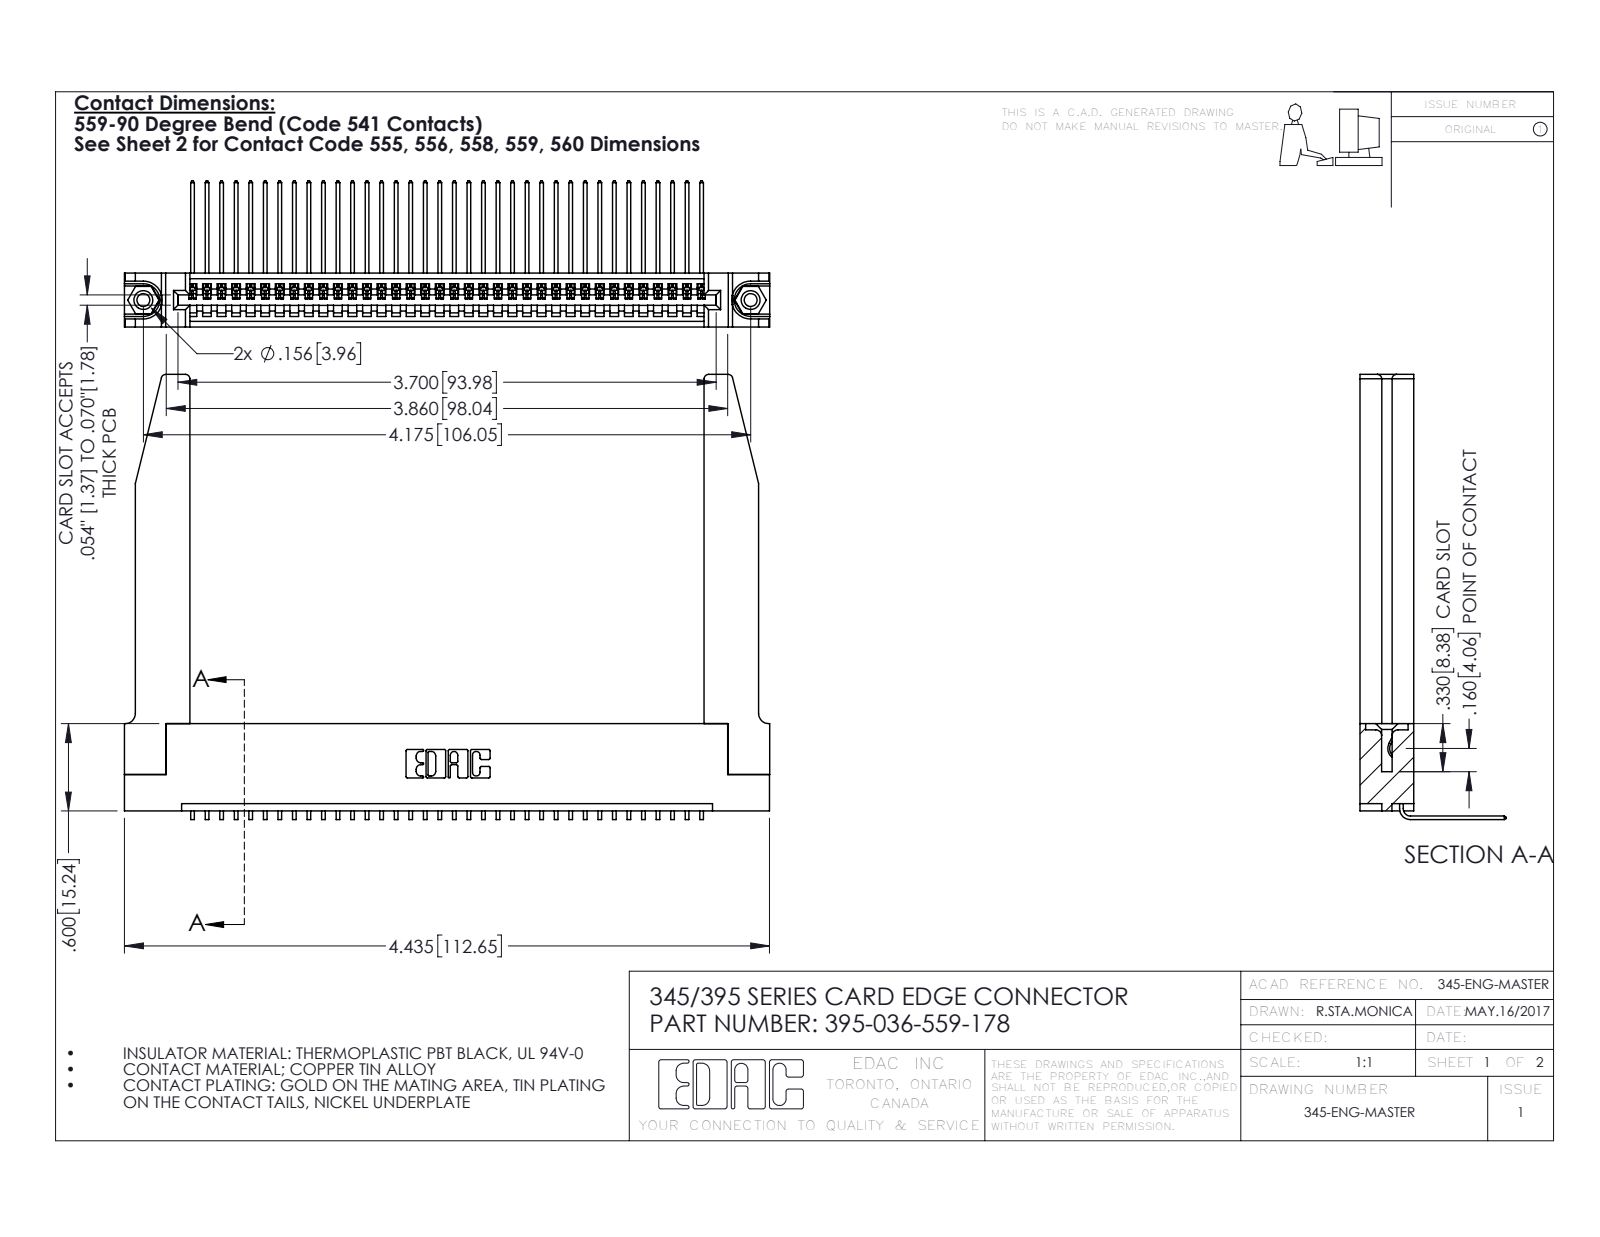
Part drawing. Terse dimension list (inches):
name: 345-292-001_558 559 Tail - 1; 345-250-001_345-250-001-102; 345 Part_Flush Mounting Lugs - 0.156 Dia-TH; 395-036-559-178 (+1 more)
written by: SolidWorks 2016 (CONFIG_CONTROL_DESIGN)
unit: in
bodies: 41 solids, 2520 faces (1734 planar, 734 cylindrical, 52 other)
size: 4.436 × 3.059 × 1.005
volume: 1.132 in³; area: 33.77 in²
holes: 2× ⌀0.089, 2× ⌀0.125, 2× ⌀0.156, 1× ⌀0.064
bosses: 2× ⌀0.155
rounds: 72× R0.006, 22× R0.01, 8× R0.03, 6× R0.007, 6× R0.031, 3× R0.026, 2× R0.031, 2× R0.04
face distances: 0.37, 0.072, 0.298, 0.2, 0.098, 0.272, 0.025, 0.225, 0.148, 0.15
hole spacings: 0.27, 3.939, 4.175
